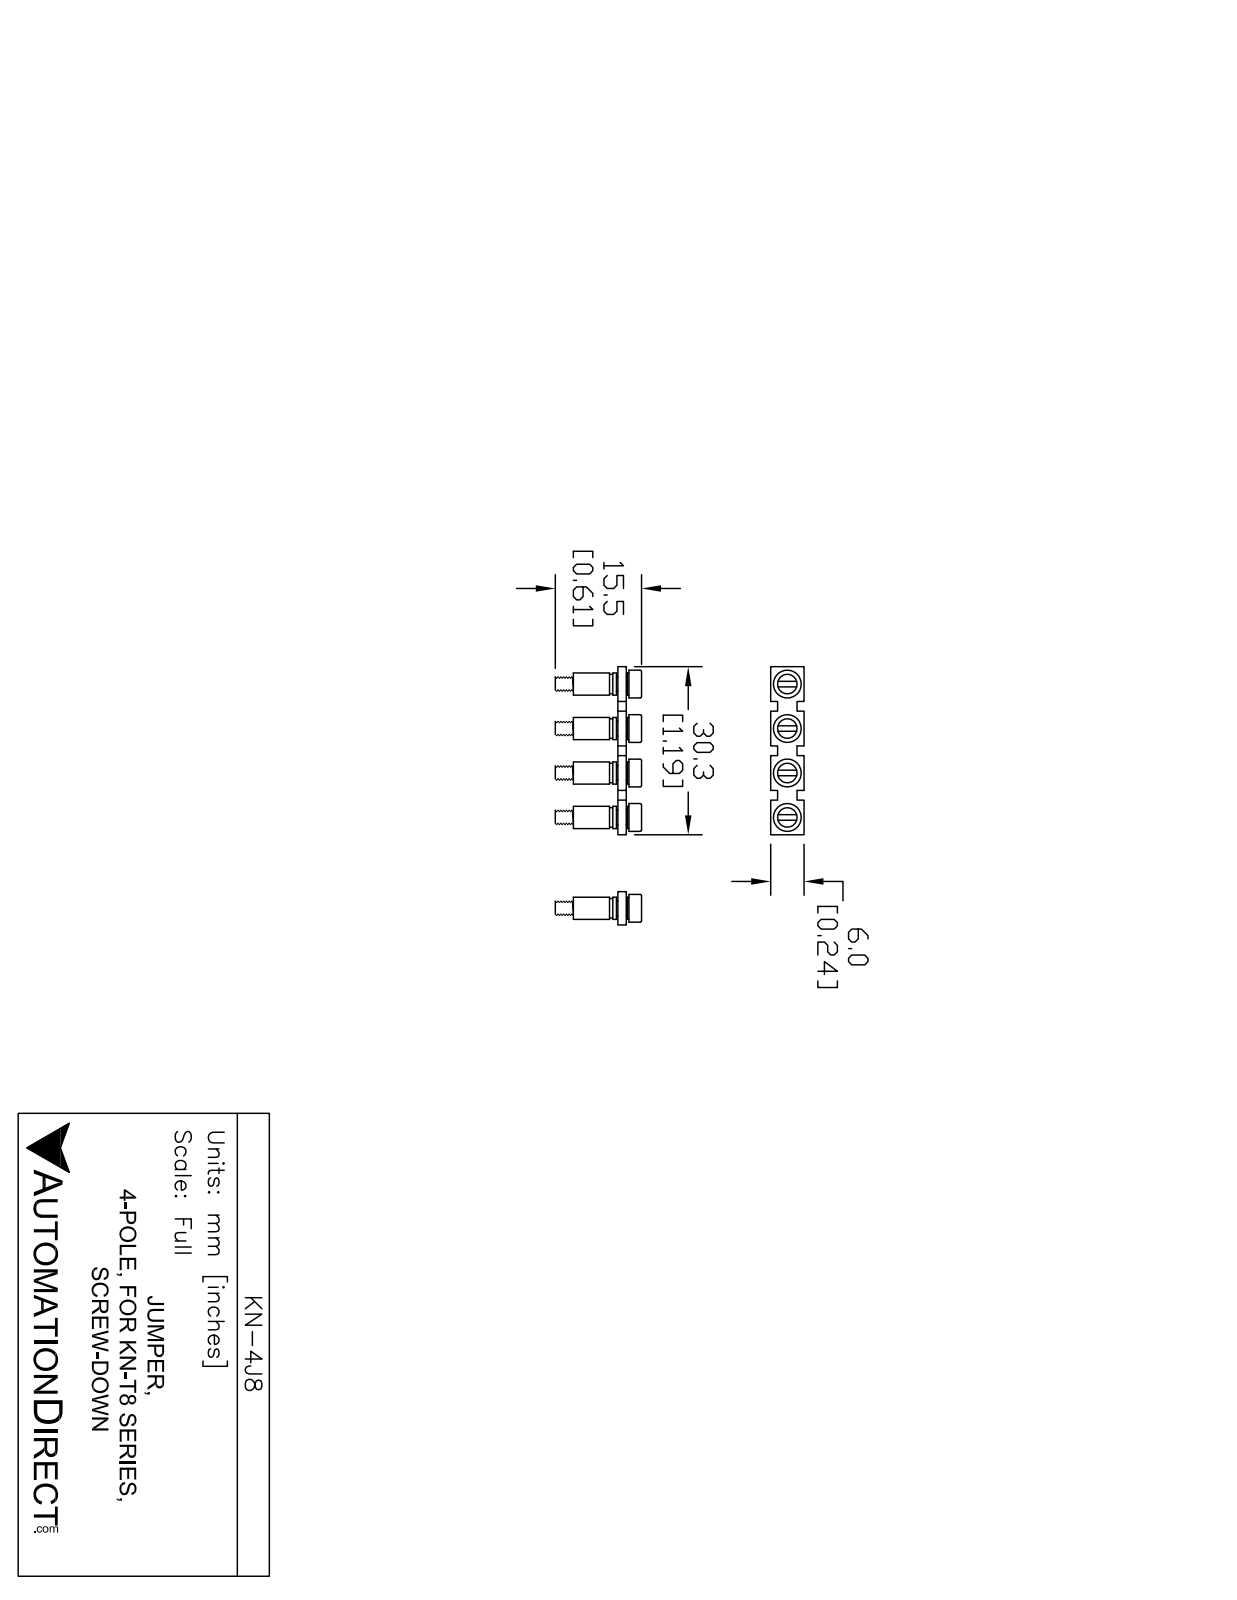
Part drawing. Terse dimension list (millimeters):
name: KN-4J8
written by: SolidWorks 2014 (AUTOMOTIVE_DESIGN)
unit: mm
bodies: 13 solids, 202 faces (94 planar, 84 cylindrical, 24 other)
size: 30.25 × 15.5 × 6
volume: 811 mm³; area: 2 225 mm²
holes: 4× ⌀2.8, 4× ⌀3, 4× ⌀3.15, 4× ⌀3.5
bosses: 4× ⌀5, 4× ⌀4, 4× ⌀2.65
face distances: 1.5, 2, 1.75, 2.25, 8, 0.5, 1, 1.25, 2.75, 6
hole spacings: 8, 16, 24
